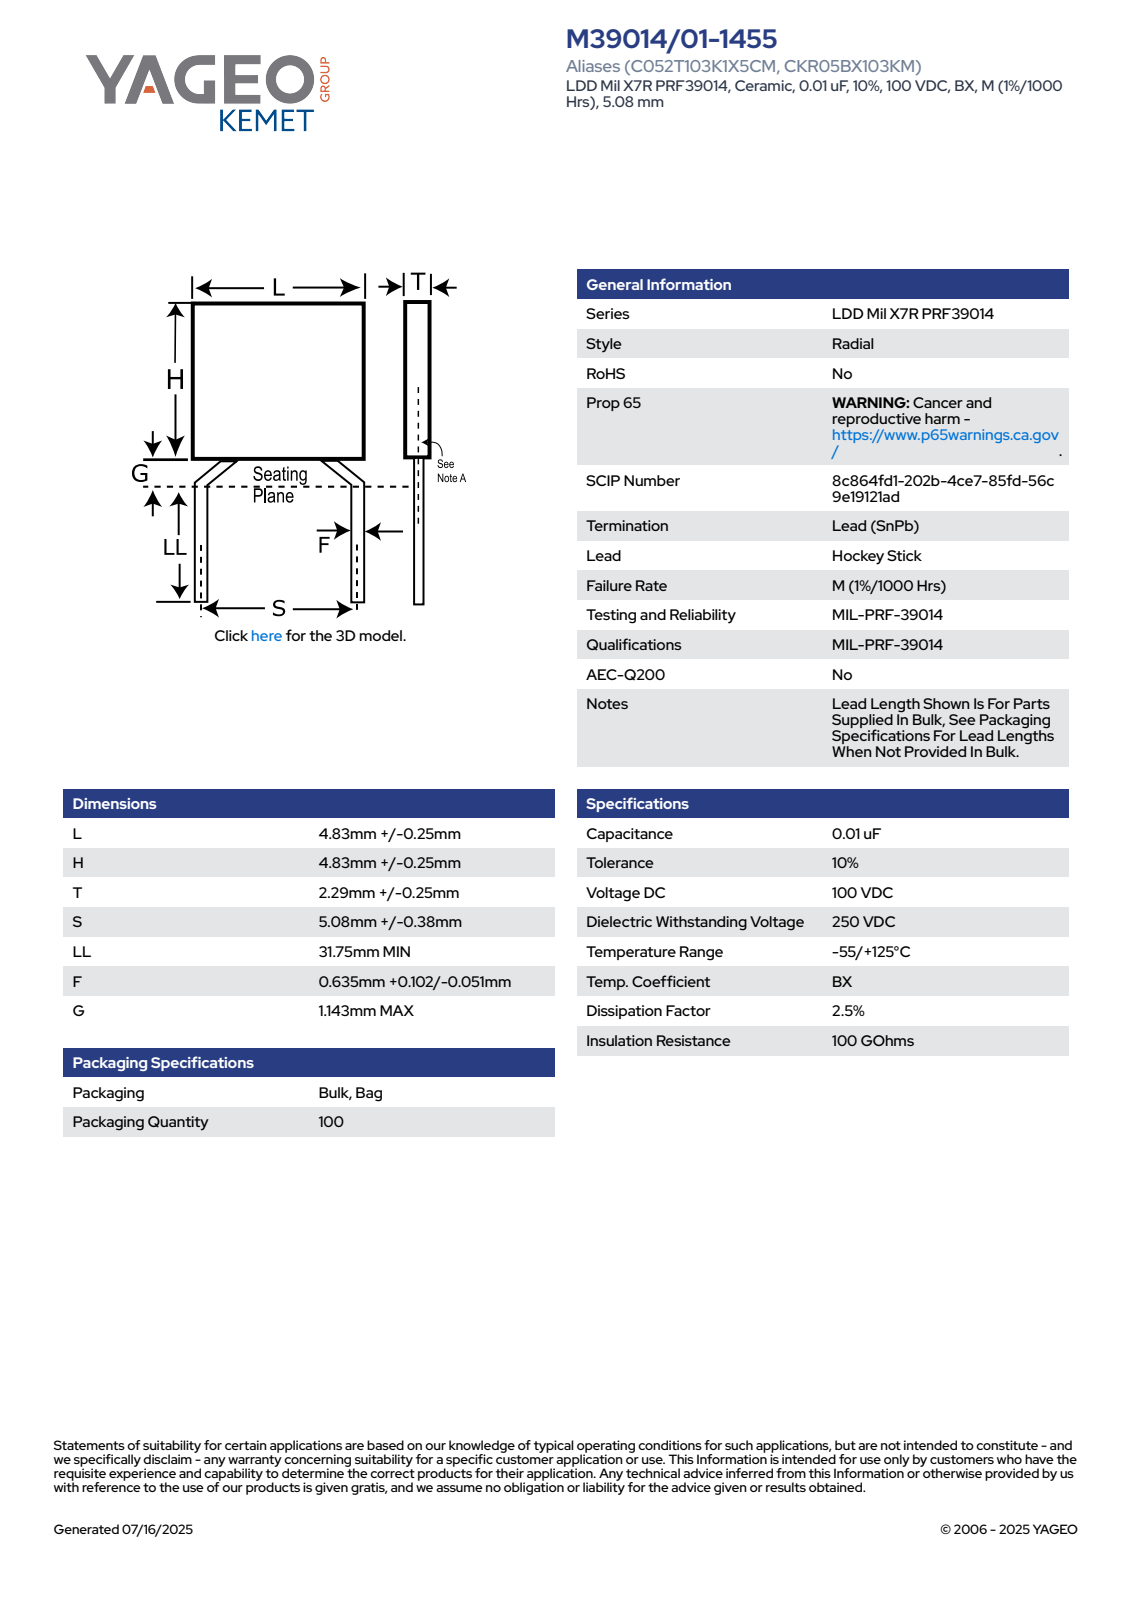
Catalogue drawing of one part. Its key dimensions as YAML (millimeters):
part_name: "CCRM_HS_C052_L5.08H5.08T2.54S5.08LL31.75F0.737G1.143K5.08"
step_written_by: "SolidWorks 2014 (AUTOMOTIVE_DESIGN)"
units: millimeters
bodies: {solids: 4, faces: 73, planar: 65, cylindrical: 4, other: 4}
overall_size: [37.97, 5.82, 2.54]
volume: 94
surface_area: 262
round_bosses_or_shafts:
  - {diameter: 0.74, count: 2}
face_to_face_distances: [2.54, 5.08, 32.89, 37.97, 2.09, 2.99, 35.88, 2.08, 34.97, 0.91]
